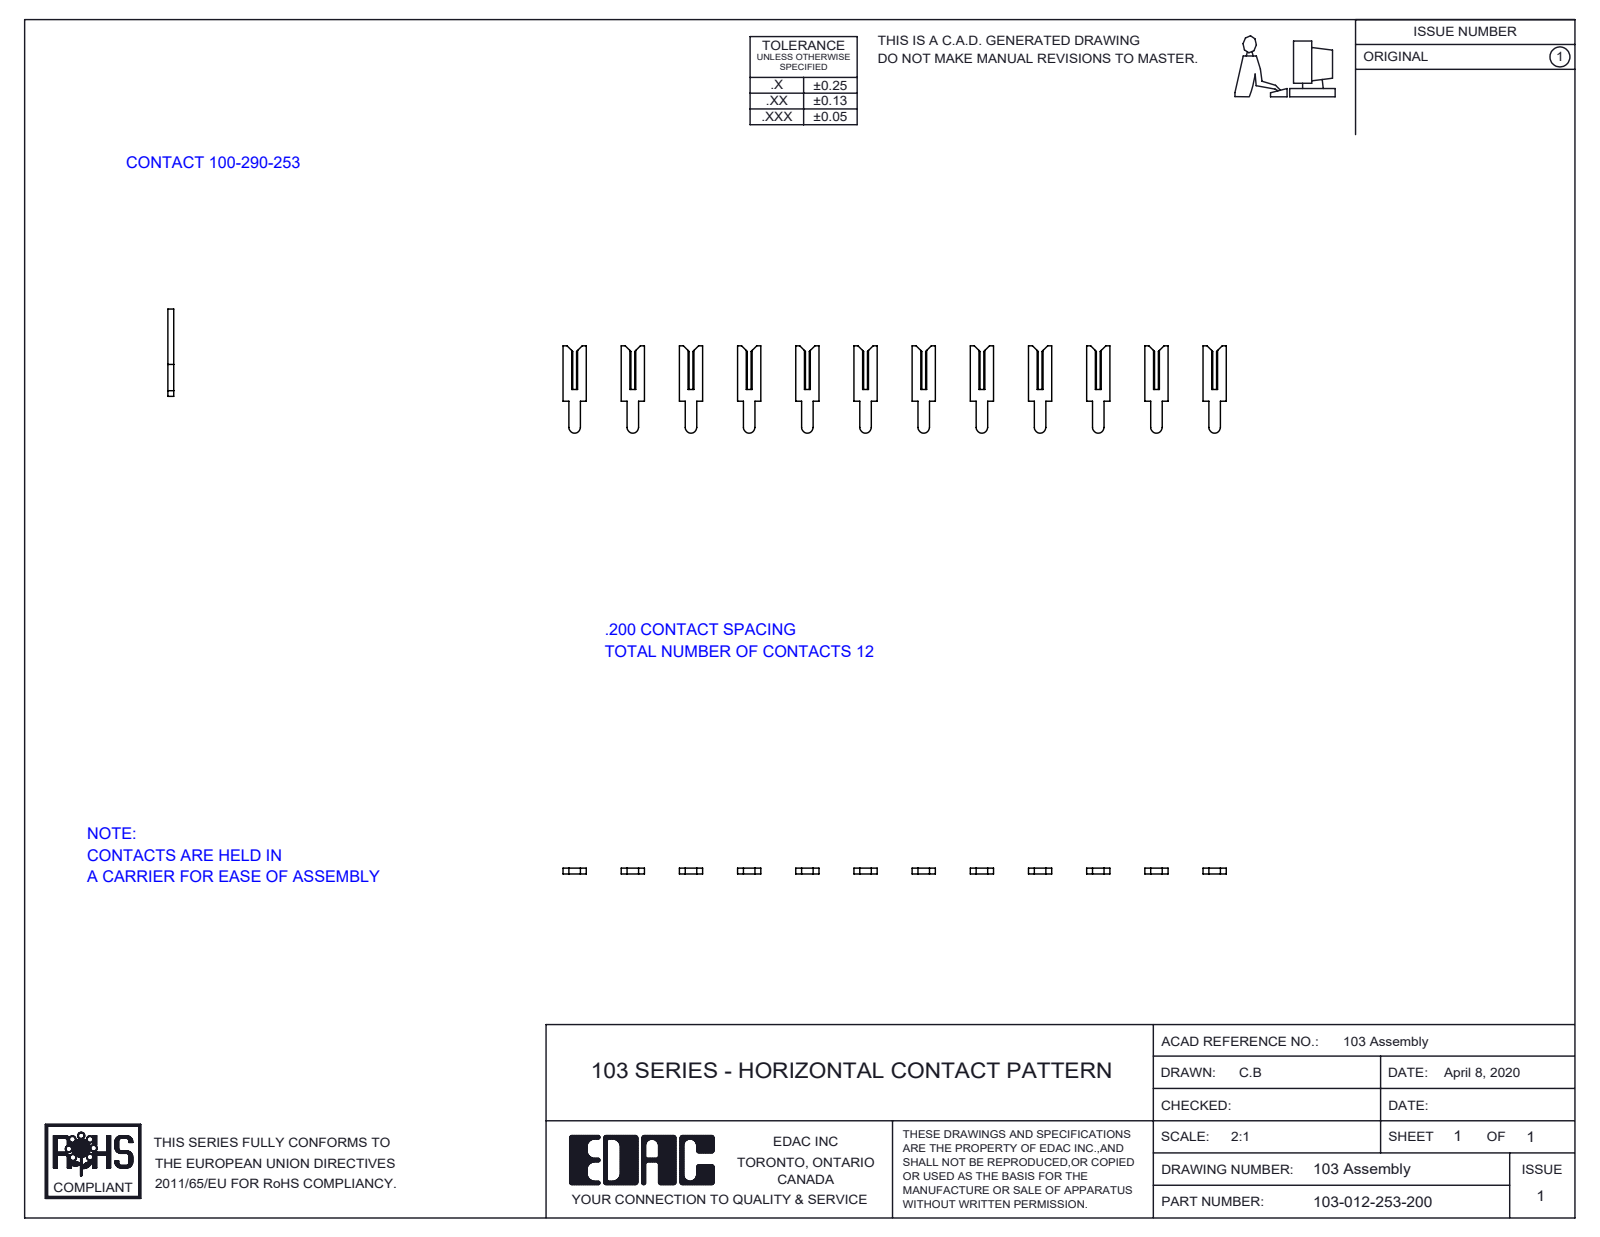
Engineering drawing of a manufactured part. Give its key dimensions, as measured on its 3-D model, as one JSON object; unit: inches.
{"part_name": "103-012-253-200; 100-290-001_100-290-253", "step_written_by": "SolidWorks 2016 (CONFIG_CONTROL_DESIGN)", "units": "inches", "bodies": {"solids": 12, "faces": 240, "planar": 228, "cylindrical": 12, "other": 0}, "overall_size": [2.28, 0.3, 0.02], "volume_in3": 0.004, "surface_area_in2": 0.64, "partial_cylinders_radius": [[0.019, 12]], "face_to_face_distances": [0.02, 0.2, 0.4, 0.6, 0.8, 1, 0.141, 1.2, 0.08, 0.28]}
